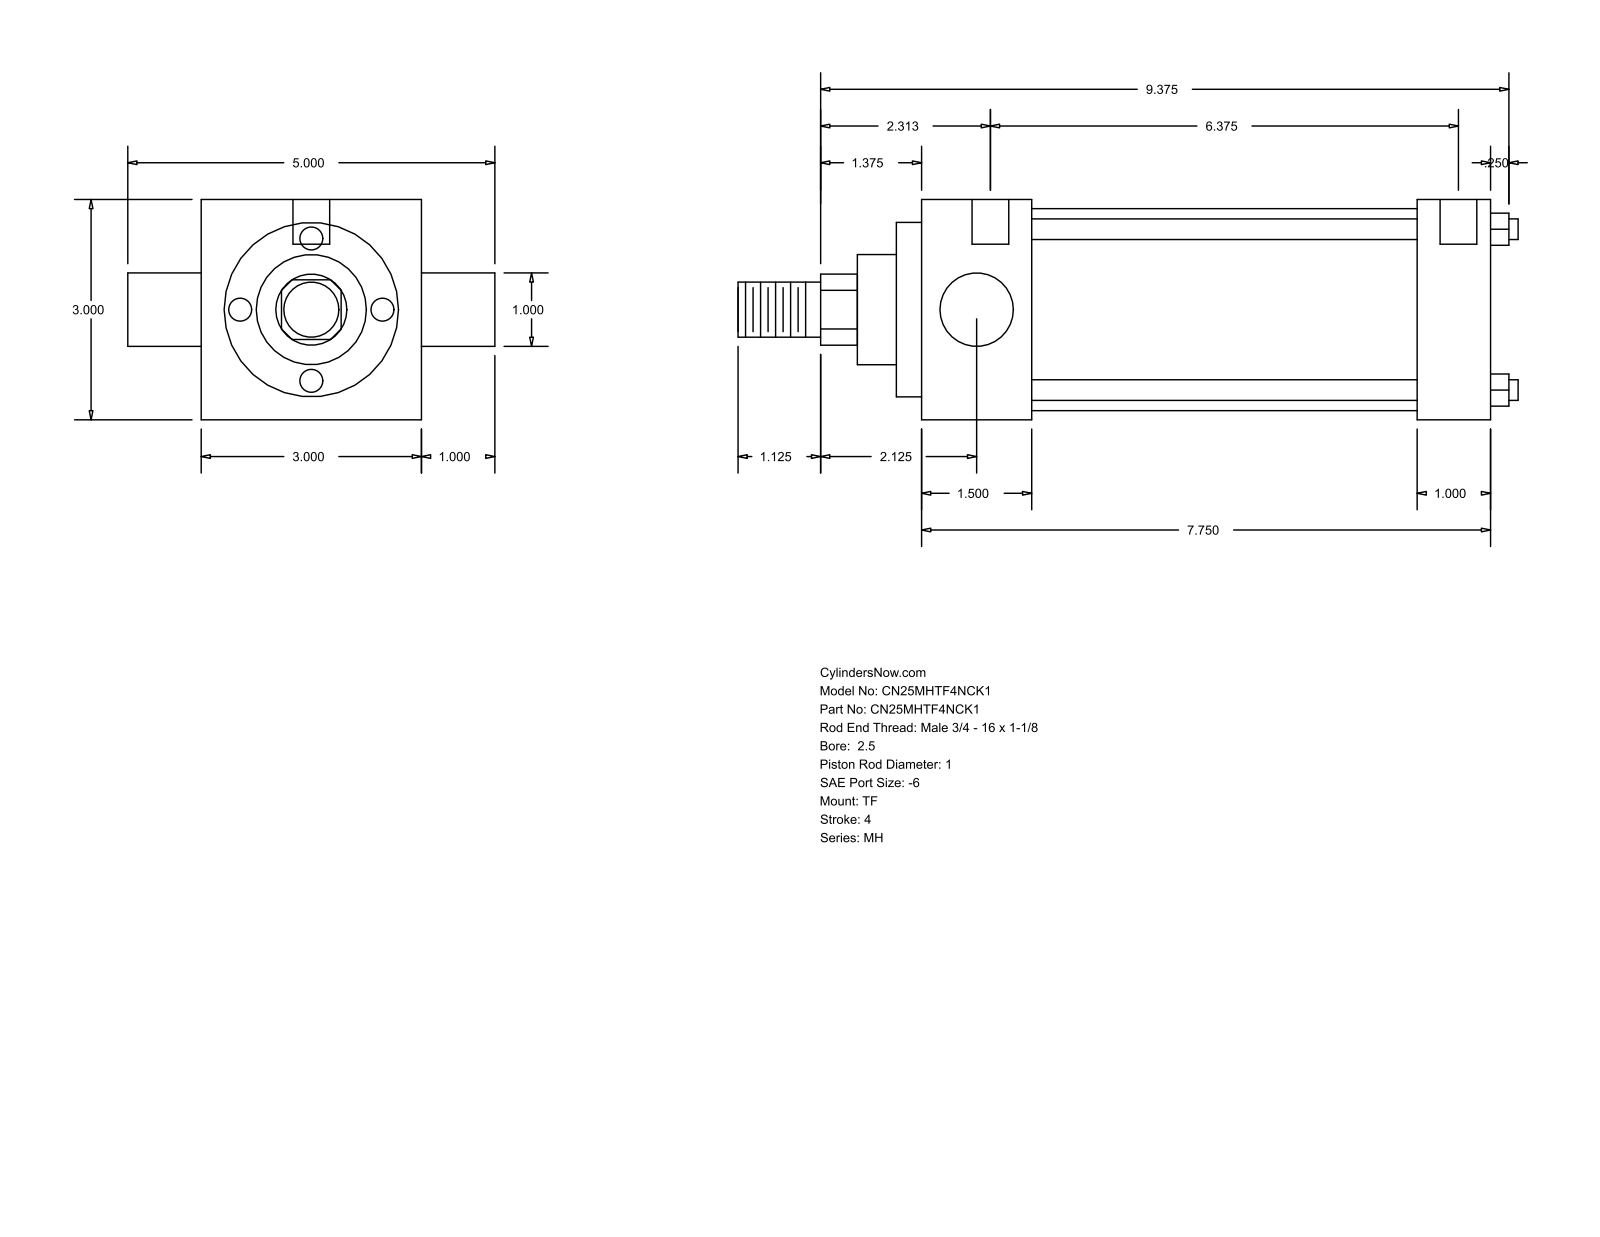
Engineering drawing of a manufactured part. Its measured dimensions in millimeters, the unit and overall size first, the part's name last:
Units: millimetres
Overall size (bounding box): 269.88 × 127 × 76.2
Round holes (diameter × count): ⌀5.56 ×3, ⌀12.7 ×2
Round bosses / shafts (diameter × count): ⌀7.14 ×4, ⌀25.4 ×2, ⌀69.85 ×1, ⌀60.33 ×1, ⌀38.1 ×1, ⌀19.05 ×1
Partial cylindrical surfaces — rounded edges, fillets, slot ends (radius × count): R12.29 ×1
Main face-to-face distances: 76.2, 196.86, 25.4, 38.11, 158.75, 171.46, 133.35, 8.73, 46.84, 180.19
Hole centre spacings: 3.18, 4.76, 161.92, 165.1, 166.68, 169.86
Bodies: 0 solids, 86 faces (61 planar, 25 cylindrical, 0 other)
Part name (STEP PRODUCT): MH_TF__0250_1
STEP written by: GSSL Pune (CONFIG_CONTROL_DESIGN)
